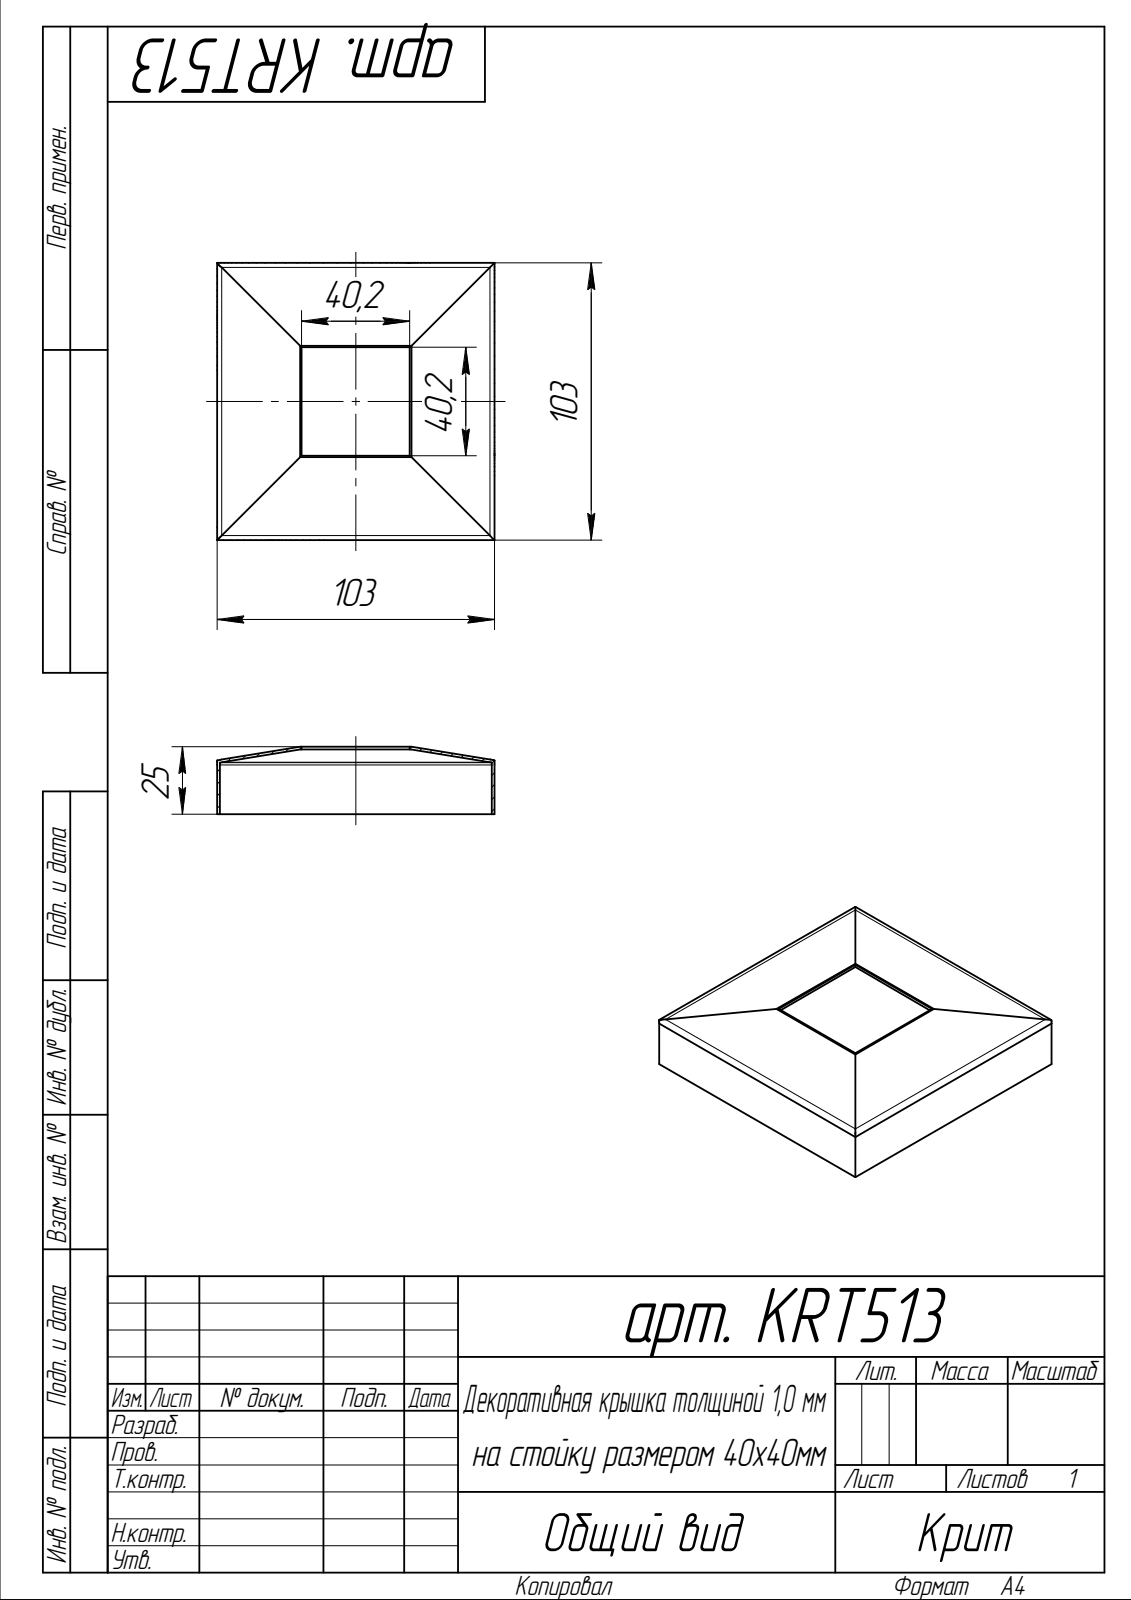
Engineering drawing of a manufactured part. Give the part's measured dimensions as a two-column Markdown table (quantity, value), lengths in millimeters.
| quantity | value |
| --- | --- |
| part name | арт. KRT513 |
| STEP written by | SolidWorks 2014 (AUTOMOTIVE_DESIGN) |
| units | millimeters |
| bodies | 1 solid, 35 faces (23 planar, 0 cylindrical, 12 other) |
| overall size | 103 × 103 × 25 |
| volume | 16 388 mm³ |
| surface area | 34 270 mm² |
| main face-to-face distances | 1, 102, 103, 101, 31.4, 71.6, 30.4, 70.6, 25, 40.2 |
